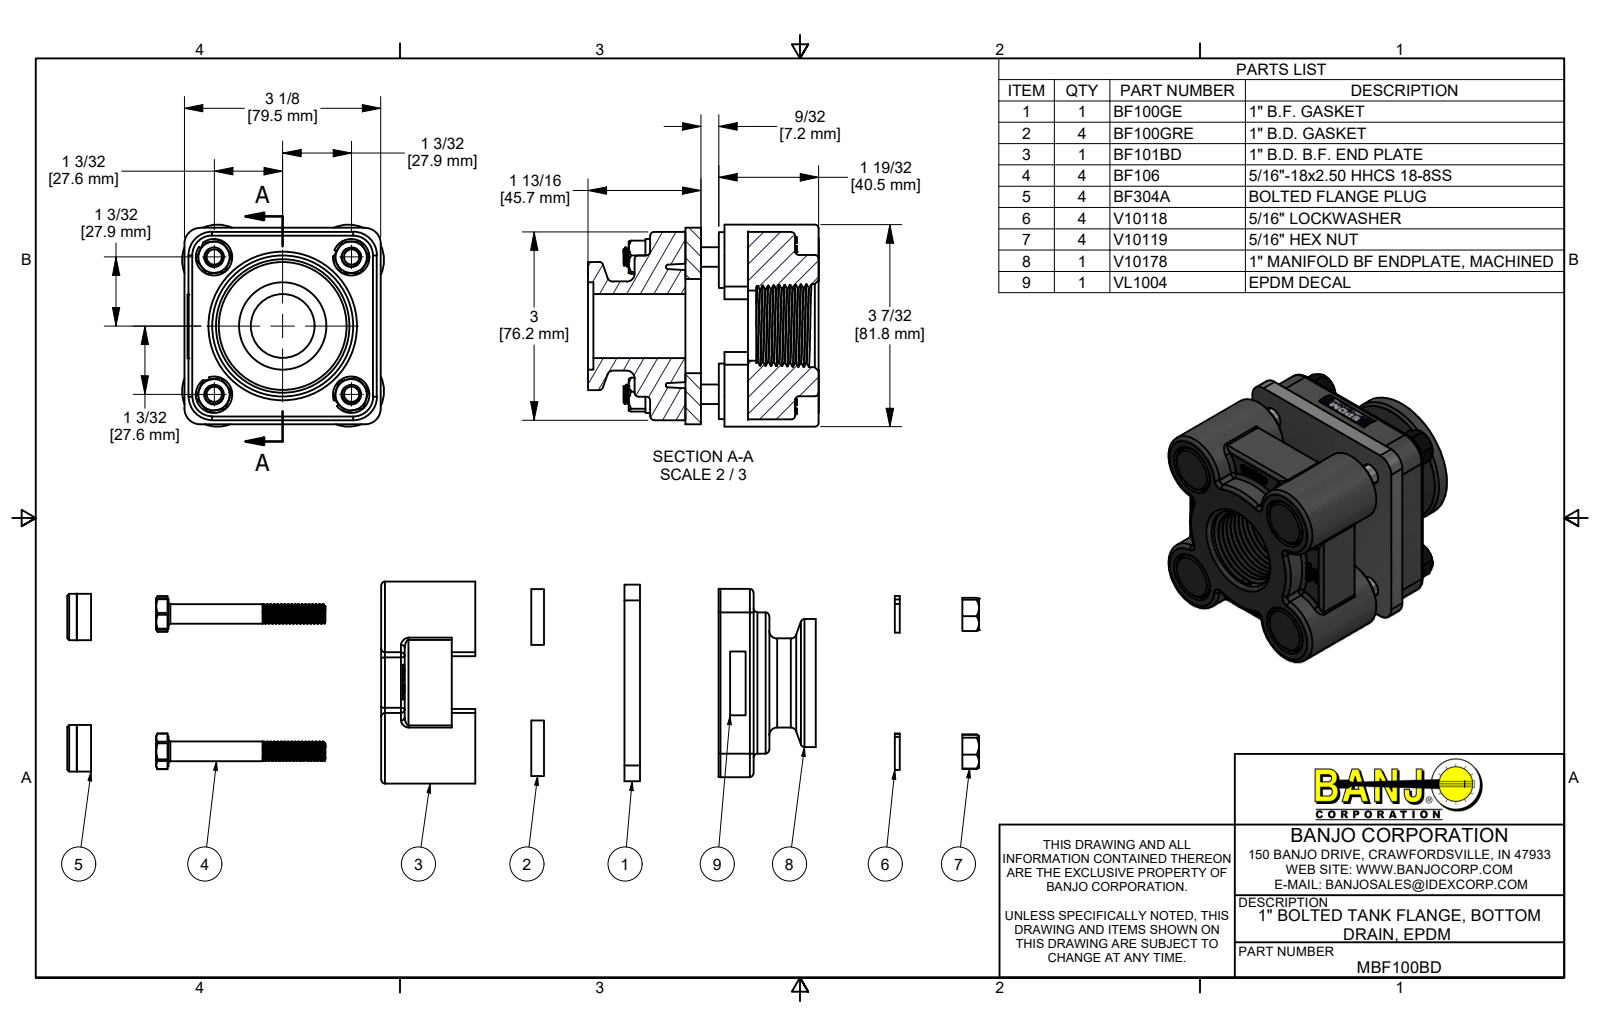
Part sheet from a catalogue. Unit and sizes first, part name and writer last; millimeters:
Units: millimetres
Overall size (bounding box): 93.34 × 81.79 × 81.79
Round holes (diameter × count): ⌀6.41 ×4, ⌀7.94 ×4, ⌀8.18 ×4, ⌀8.64 ×4, ⌀8.74 ×4, ⌀8.89 ×4, ⌀12.19 ×4, ⌀18.14 ×4, ⌀19.05 ×4, ⌀23.37 ×4, ⌀25.91 ×1, ⌀28.45 ×1
Round bosses / shafts (diameter × count): ⌀22.5 ×4, ⌀18.85 ×4, ⌀14.81 ×4, ⌀12.7 ×4, ⌀12.19 ×4, ⌀7.94 ×4, ⌀7.75 ×4, ⌀6.22 ×4
Partial cylindrical surfaces — rounded edges, fillets, slot ends (radius × count): R1.52 ×28, R0.76 ×24, R1.59 ×4, R6.35 ×4, R9.53 ×4, R14.35 ×4, R10.01 ×1, R13.13 ×1
Main face-to-face distances: 6.35, 6.36, 19.05, 20.58, 47.62, 53.98, 53.97, 68.2, 14.22, 14.23
Hole centre spacings: 54.4, 55.73, 37.53, 39.3, 39.37, 39.51, 55.68, 55.88
Volume: 305 421 mm³ · Surface area: 96 228 mm²
Bodies: 24 solids, 1030 faces (469 planar, 230 cylindrical, 331 other)
Part name (STEP PRODUCT): BF101BD; BF100GE; BF100GRE; BF106 (+8 more)
STEP written by: Autodesk Inventor 2014 (AUTOMOTIVE_DESIGN)
